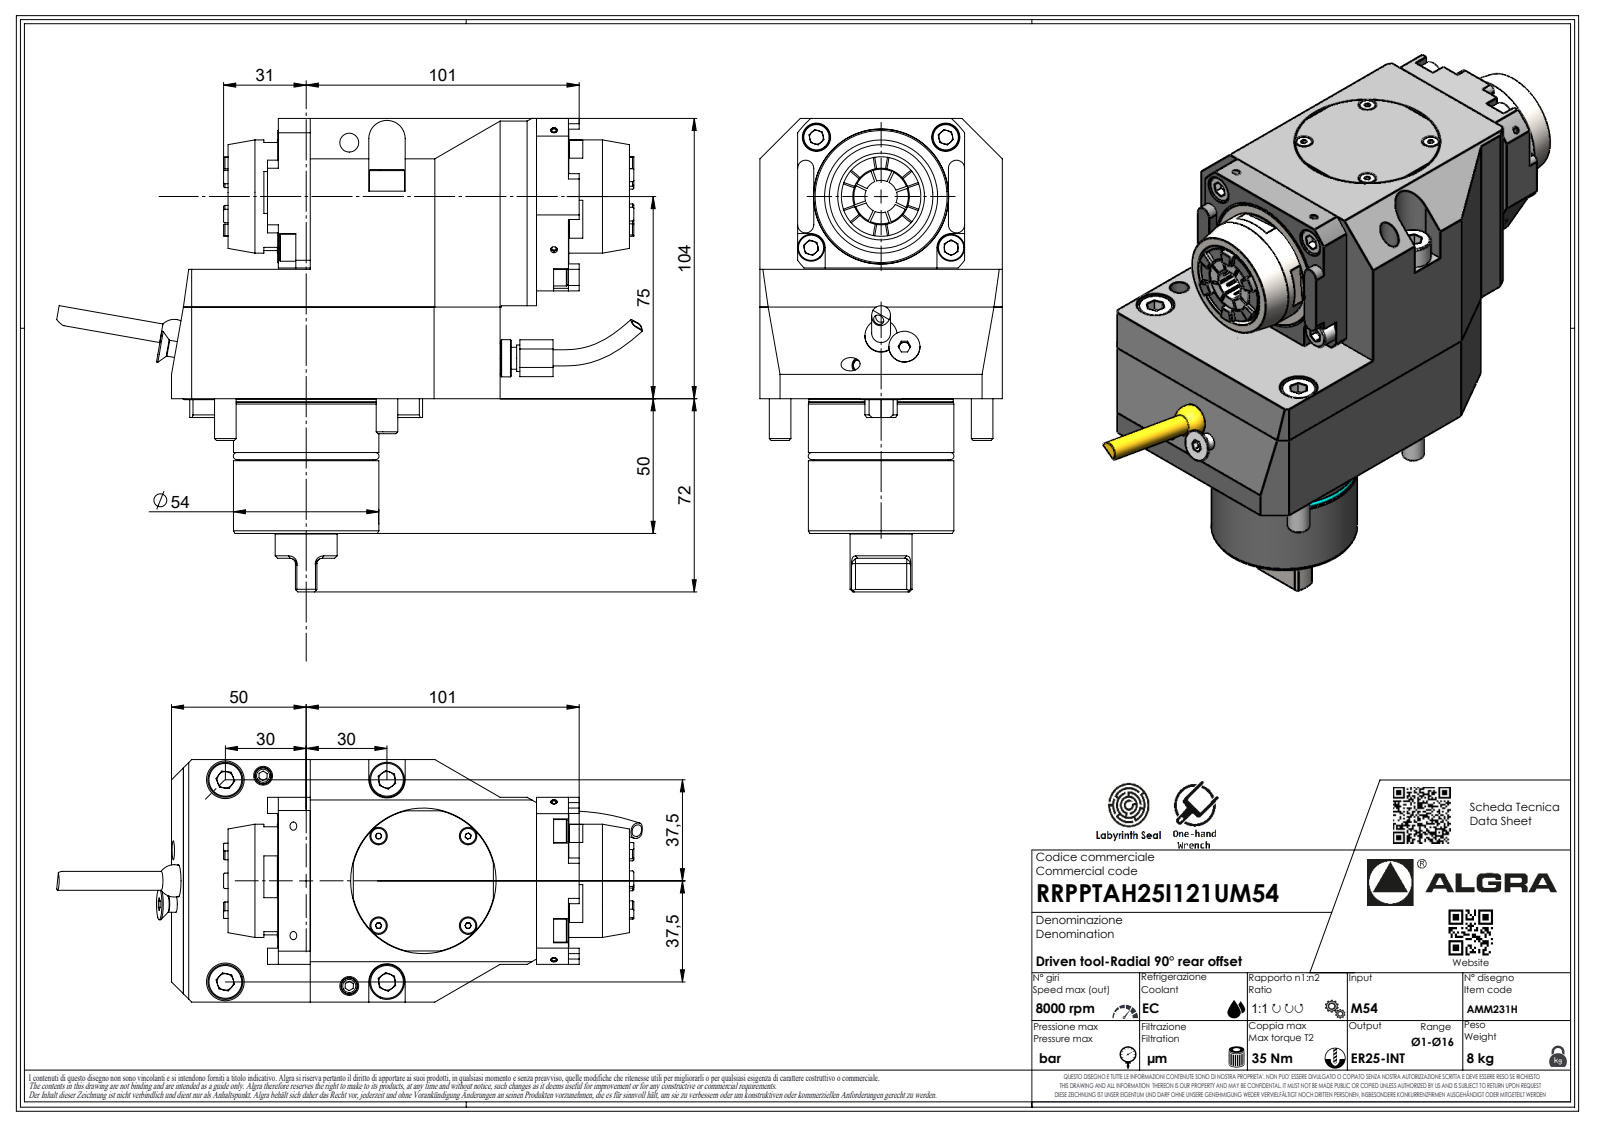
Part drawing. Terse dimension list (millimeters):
name: RRPPTAH25I121UM54
written by: SolidWorks 2023 (AUTOMOTIVE_DESIGN)
unit: mm
bodies: 1 solid, 576 faces (405 planar, 79 cylindrical, 92 other)
size: 217.42 × 175.7 × 90
volume: 1 144 000 mm³; area: 83 652 mm²
holes: 1× ⌀2.1, 1× ⌀4
bosses: 1× ⌀54, 1× ⌀53.6, 1× ⌀49.9, 1× ⌀42, 1× ⌀23, 1× ⌀9.8, 1× ⌀8.15, 1× ⌀7
rounds: 19× R2, 7× R0.33, 7× R0.52, 7× R3.7, 4× R3, 2× R6, 1× R0.21, 1× R25.1
face distances: 90, 104, 48, 14, 56, 76, 11.85, 50, 62, 95.85
